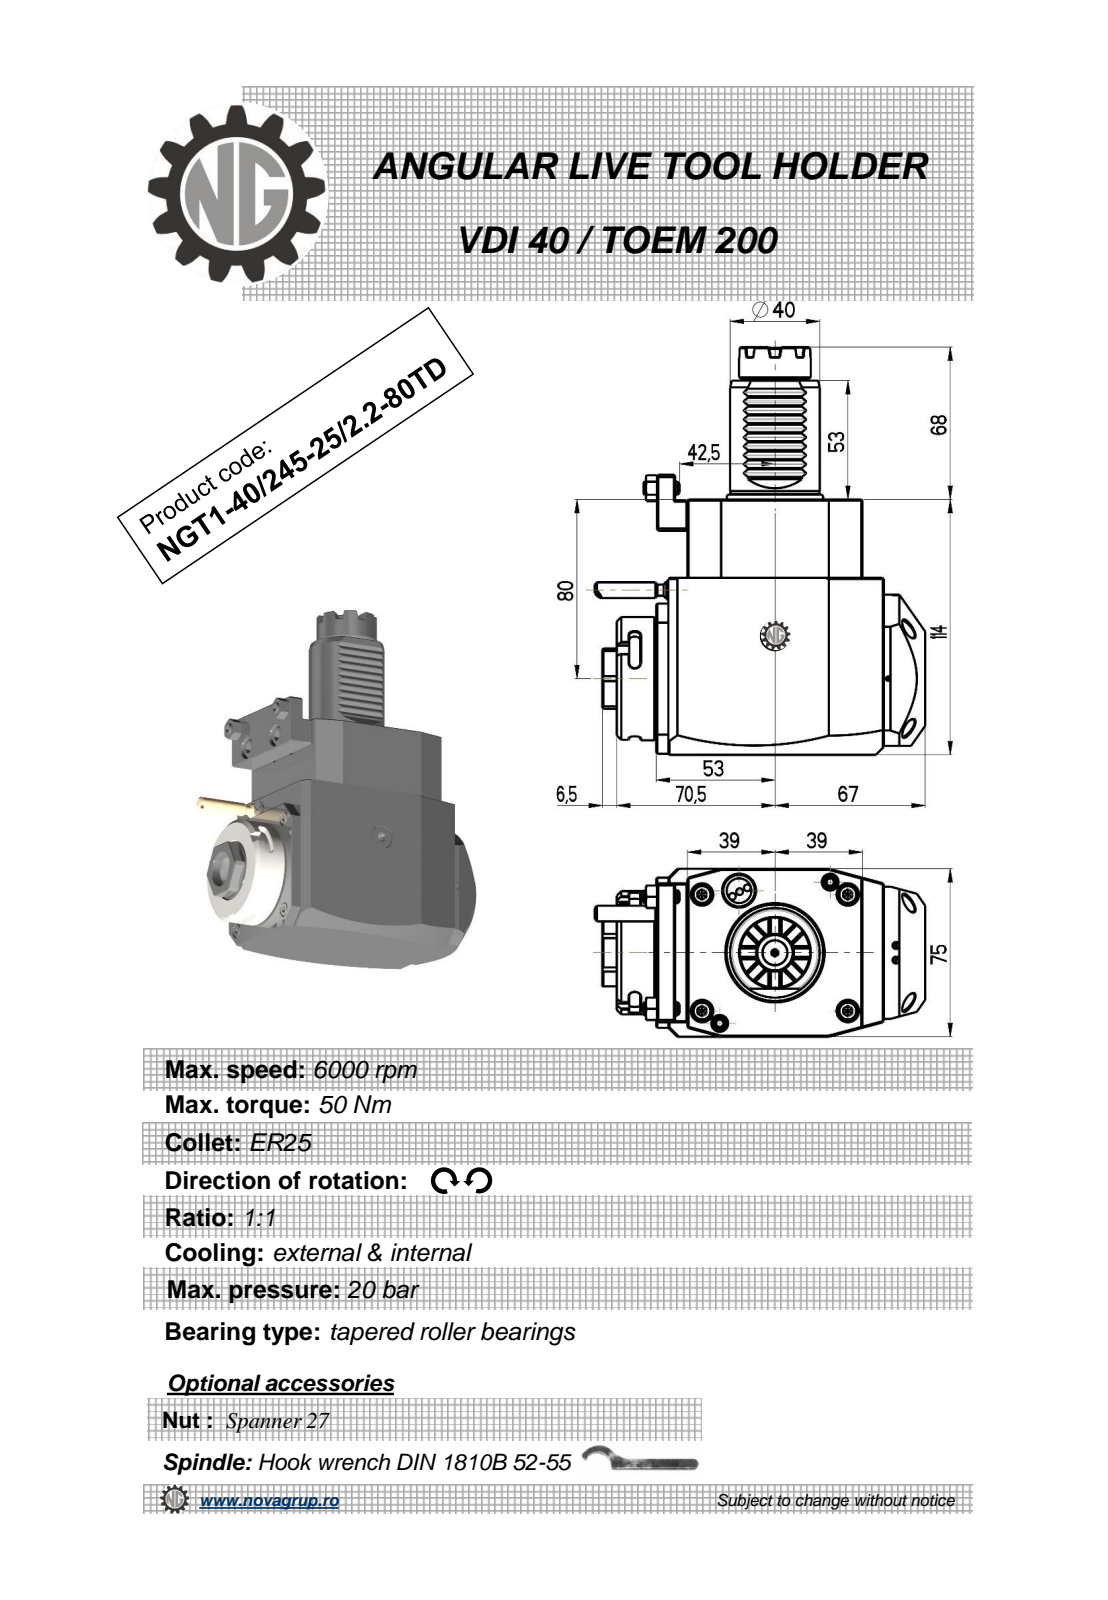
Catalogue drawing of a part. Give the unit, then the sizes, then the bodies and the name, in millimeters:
Units: millimetres
Overall size (bounding box): 182 × 147.33 × 75
Round holes (diameter × count): ⌀2.5 ×1, ⌀3 ×1, ⌀18 ×1
Round bosses / shafts (diameter × count): ⌀6 ×2, ⌀55 ×1, ⌀48 ×1, ⌀40 ×1, ⌀32 ×1, ⌀17.2 ×1, ⌀8 ×1, ⌀7 ×1
Partial cylindrical surfaces — rounded edges, fillets, slot ends (radius × count): R0.3 ×10, R0.31 ×10, R2.5 ×6, R180 ×2, R0.5 ×1, R15 ×1, R24.5 ×1, R37.5 ×1
Main face-to-face distances: 75, 114, 0.5, 14, 92, 109.5, 17.5, 13.5, 5.5, 31.5
Hole centre spacings: 43.2
Volume: 963 901 mm³ · Surface area: 72 544 mm²
Bodies: 1 solid, 421 faces (219 planar, 72 cylindrical, 130 other)
Part name (STEP PRODUCT): NGT1_40_245_25_1_2_80TD
STEP written by: PRO/ENGINEER BY PARAMETRIC TECHNOLOGY CORPORATION, 2010280 (CONFIG_CONTROL_DESIGN)
